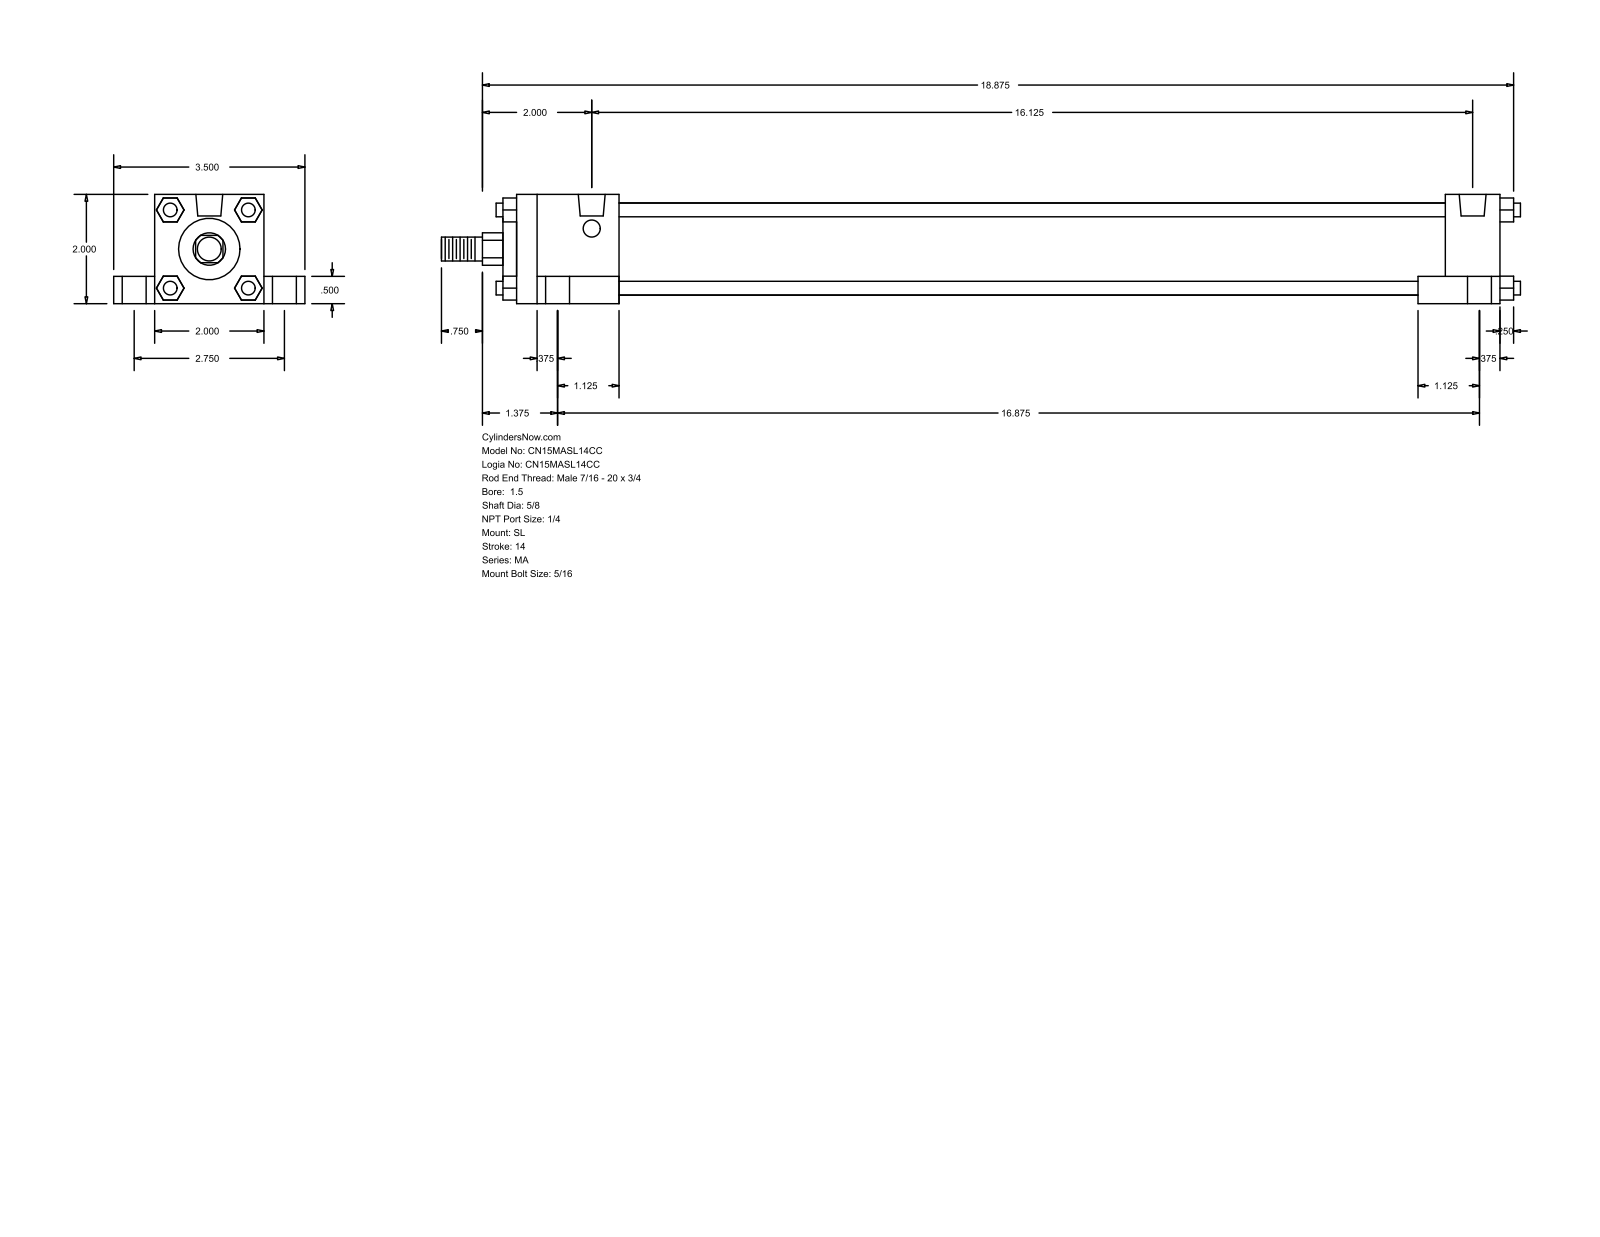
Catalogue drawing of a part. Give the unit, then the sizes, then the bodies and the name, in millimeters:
Units: millimetres
Overall size (bounding box): 501.65 × 88.9 × 50.8
Round holes (diameter × count): ⌀7.94 ×4, ⌀11.11 ×4, ⌀17.46 ×4, ⌀12.49 ×2
Round bosses / shafts (diameter × count): ⌀6.35 ×4, ⌀42.93 ×1, ⌀28.57 ×1, ⌀15.88 ×1, ⌀11.11 ×1
Partial cylindrical surfaces — rounded edges, fillets, slot ends (radius × count): R7.54 ×1
Main face-to-face distances: 50.8, 19.05, 38.1, 69.85, 12.7, 457.19, 9.52, 431.8, 25.39, 47.62
Hole centre spacings: 35.06, 38.36, 69.84, 409.58, 414.22, 426.89, 428.63, 434.28
Bodies: 0 solids, 148 faces (112 planar, 36 cylindrical, 0 other)
Part name (STEP PRODUCT): MA_SL__0150_0.625
STEP written by: GSSL Pune (CONFIG_CONTROL_DESIGN)
